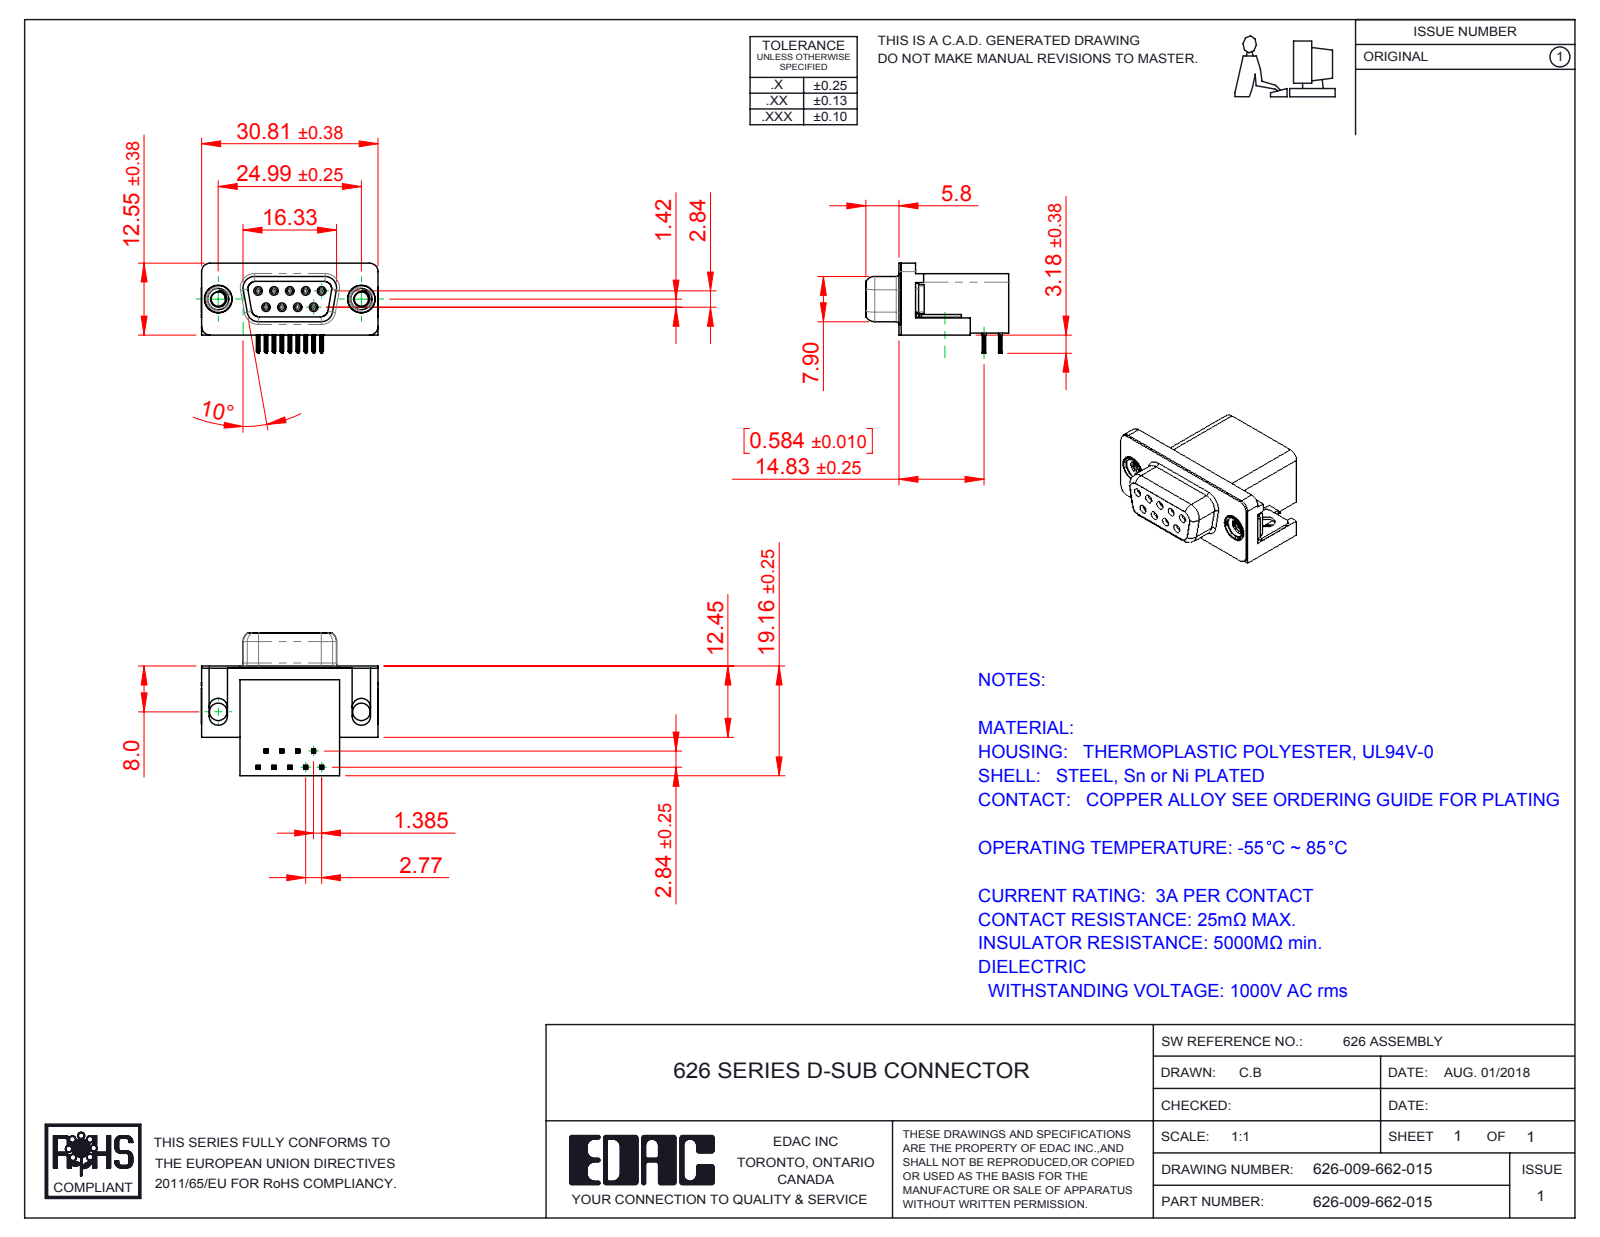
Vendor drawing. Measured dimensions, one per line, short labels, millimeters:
name: 626 M3 Threaded Rivet; 626-009-662-015; 626 Contact Top; 626 Shell_9 Socket (+3 more)
written by: SolidWorks 2016 (CONFIG_CONTROL_DESIGN)
unit: mm
bodies: 15 solids, 1572 faces (684 planar, 420 cylindrical, 468 other)
size: 30.89 × 24.96 × 15.73
volume: 4 961 mm³; area: 5 781 mm²
holes: 9× ⌀0.8, 9× ⌀0.9, 2× ⌀2.5, 2× ⌀3.05, 2× ⌀4, 2× ⌀4.8, 2× ⌀5
bosses: 9× ⌀1.2, 2× ⌀4.9, 2× ⌀4.75, 2× ⌀3.9
rounds: 72× R0.1, 36× R0.15, 18× R0.35, 18× R1, 9× R0.34, 8× R0.25, 8× R1.35, 8× R1.6
face distances: 0.4, 10.34, 0.35, 18.76, 19.16, 2.9, 2.5, 6.2, 16.26, 0.5
hole spacings: 3.16, 2.77, 5.54, 5.03, 5.04, 8.31, 7.48, 7.49
